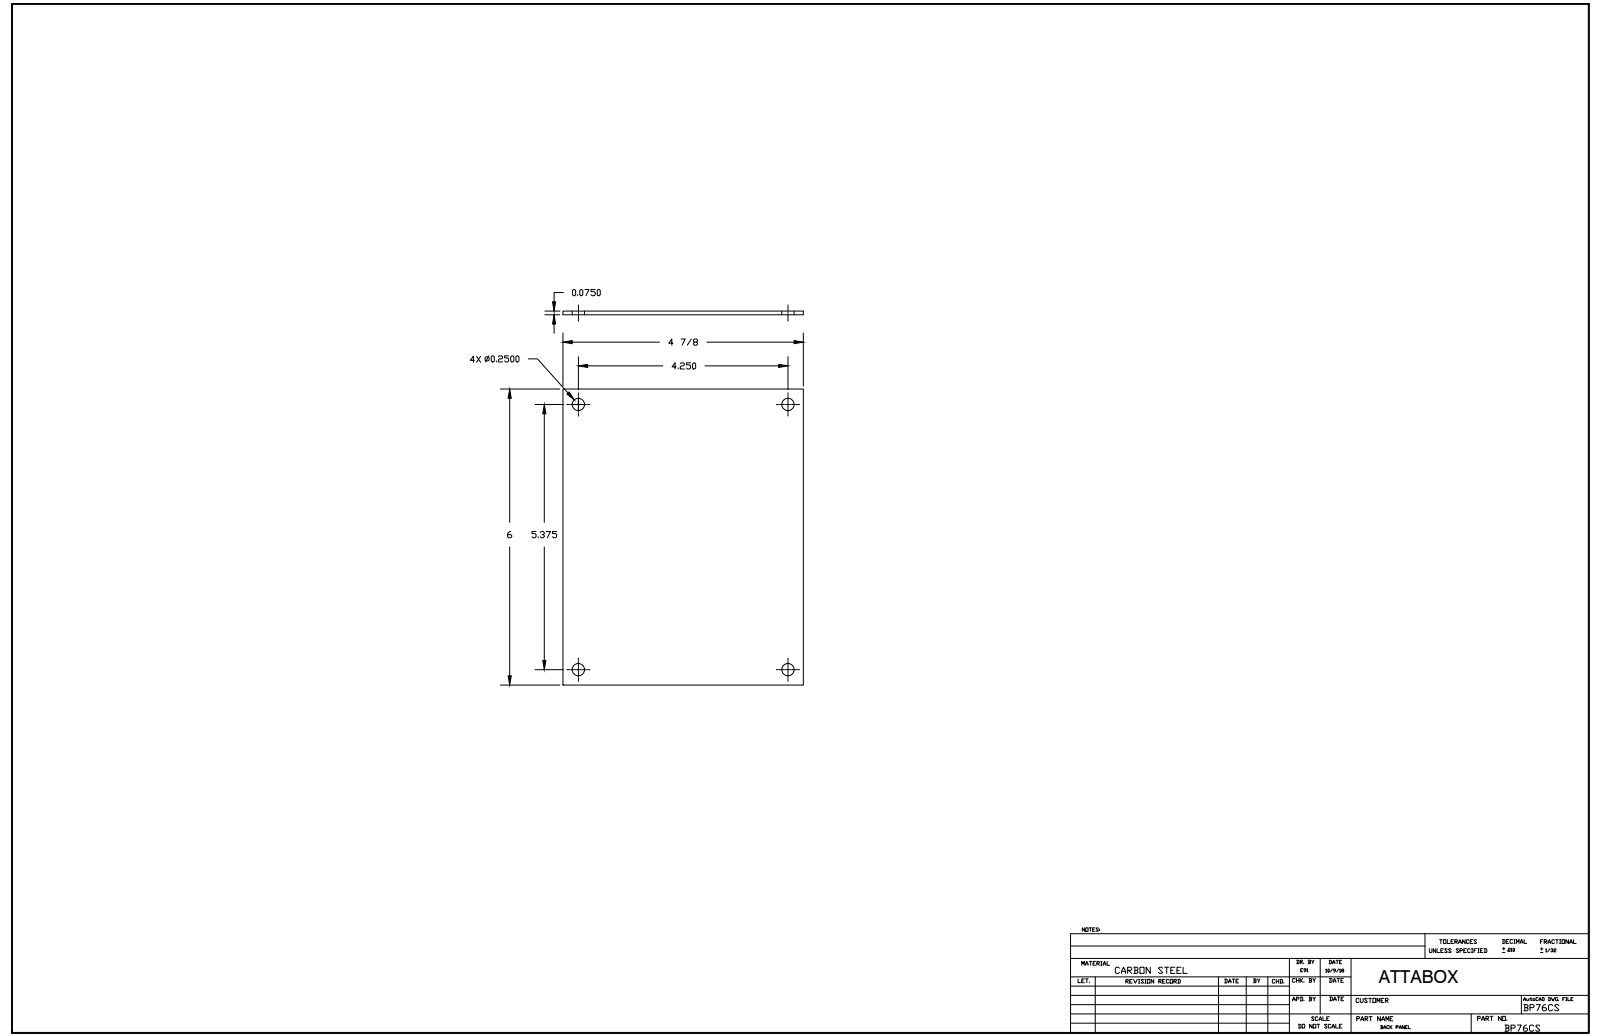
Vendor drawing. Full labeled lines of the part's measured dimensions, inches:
Part name (STEP PRODUCT): BP76CS_STP
STEP written by: Autodesk Inventor 2014 (AUTOMOTIVE_DESIGN)
Units: inches
Bodies: 1 solid, 10 faces (6 planar, 4 cylindrical, 0 other)
Overall size (bounding box): 6 × 4.88 × 0.075
Volume: 2.181 in³ · Surface area: 60.03 in²
Round holes (diameter × count): ⌀0.25 ×4
Main face-to-face distances: 0.075, 4.88, 6
Hole centre spacings: 4.25, 5.376, 6.853
